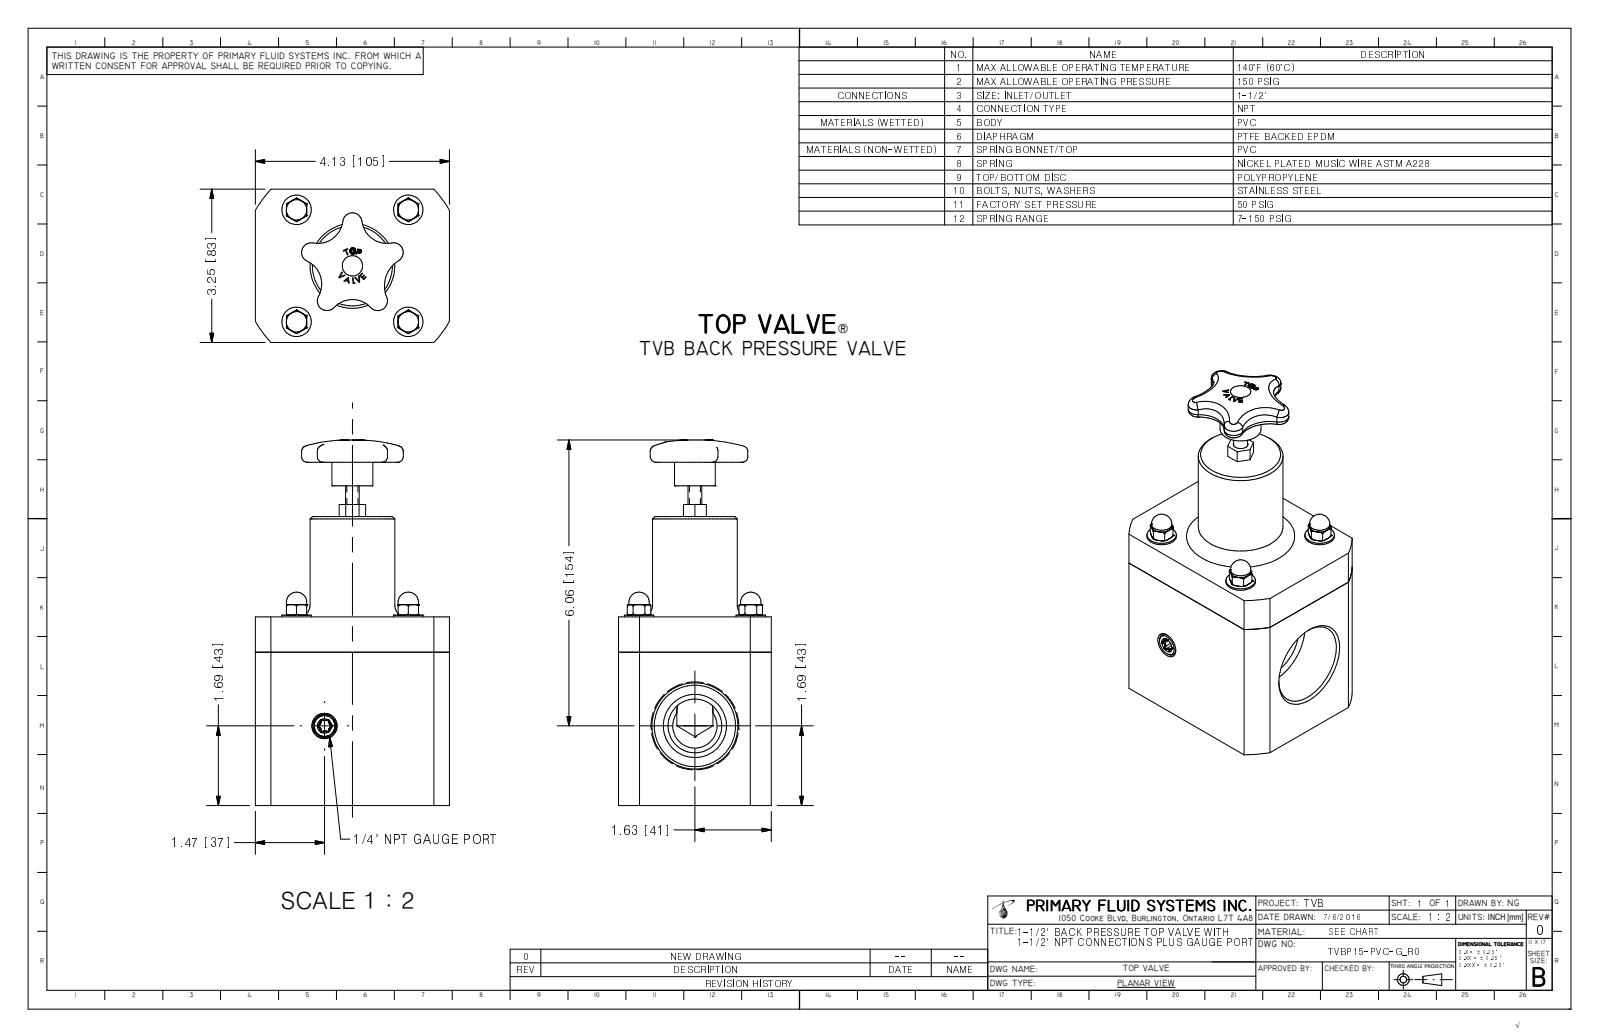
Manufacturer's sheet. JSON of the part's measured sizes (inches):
{"part_name": "TVBP15-PVC-G_R0", "step_written_by": "Autodesk Inventor 2009 (AUTOMOTIVE_DESIGN)", "units": "inches", "bodies": {"solids": 6, "faces": 413, "planar": 170, "cylindrical": 62, "other": 181}, "overall_size": [7.752, 4.125, 3.25], "volume_in3": 48.65, "surface_area_in2": 154.4, "round_holes": [[0.188, 1], [0.313, 1], [0.375, 1], [0.437, 1], [1.14, 1], [1.2, 1], [1.43, 1], [1.727, 1], [1.856, 1], [2.75, 1]], "round_bosses_or_shafts": [[0.625, 4], [0.433, 4], [0.375, 4], [0.175, 4], [1.8, 1], [1.076, 1], [0.87, 1], [0.293, 1]], "partial_cylinders_radius": [[0.027, 6], [0.085, 5], [0.205, 5], [0.536, 4], [0.656, 4], [0.625, 1], [0.745, 1], [2.375, 1]], "face_to_face_distances": [3.25, 4, 4.125, 3.25, 0.75, 2.125, 0.045, 3.205, 0.795, 6.125]}
